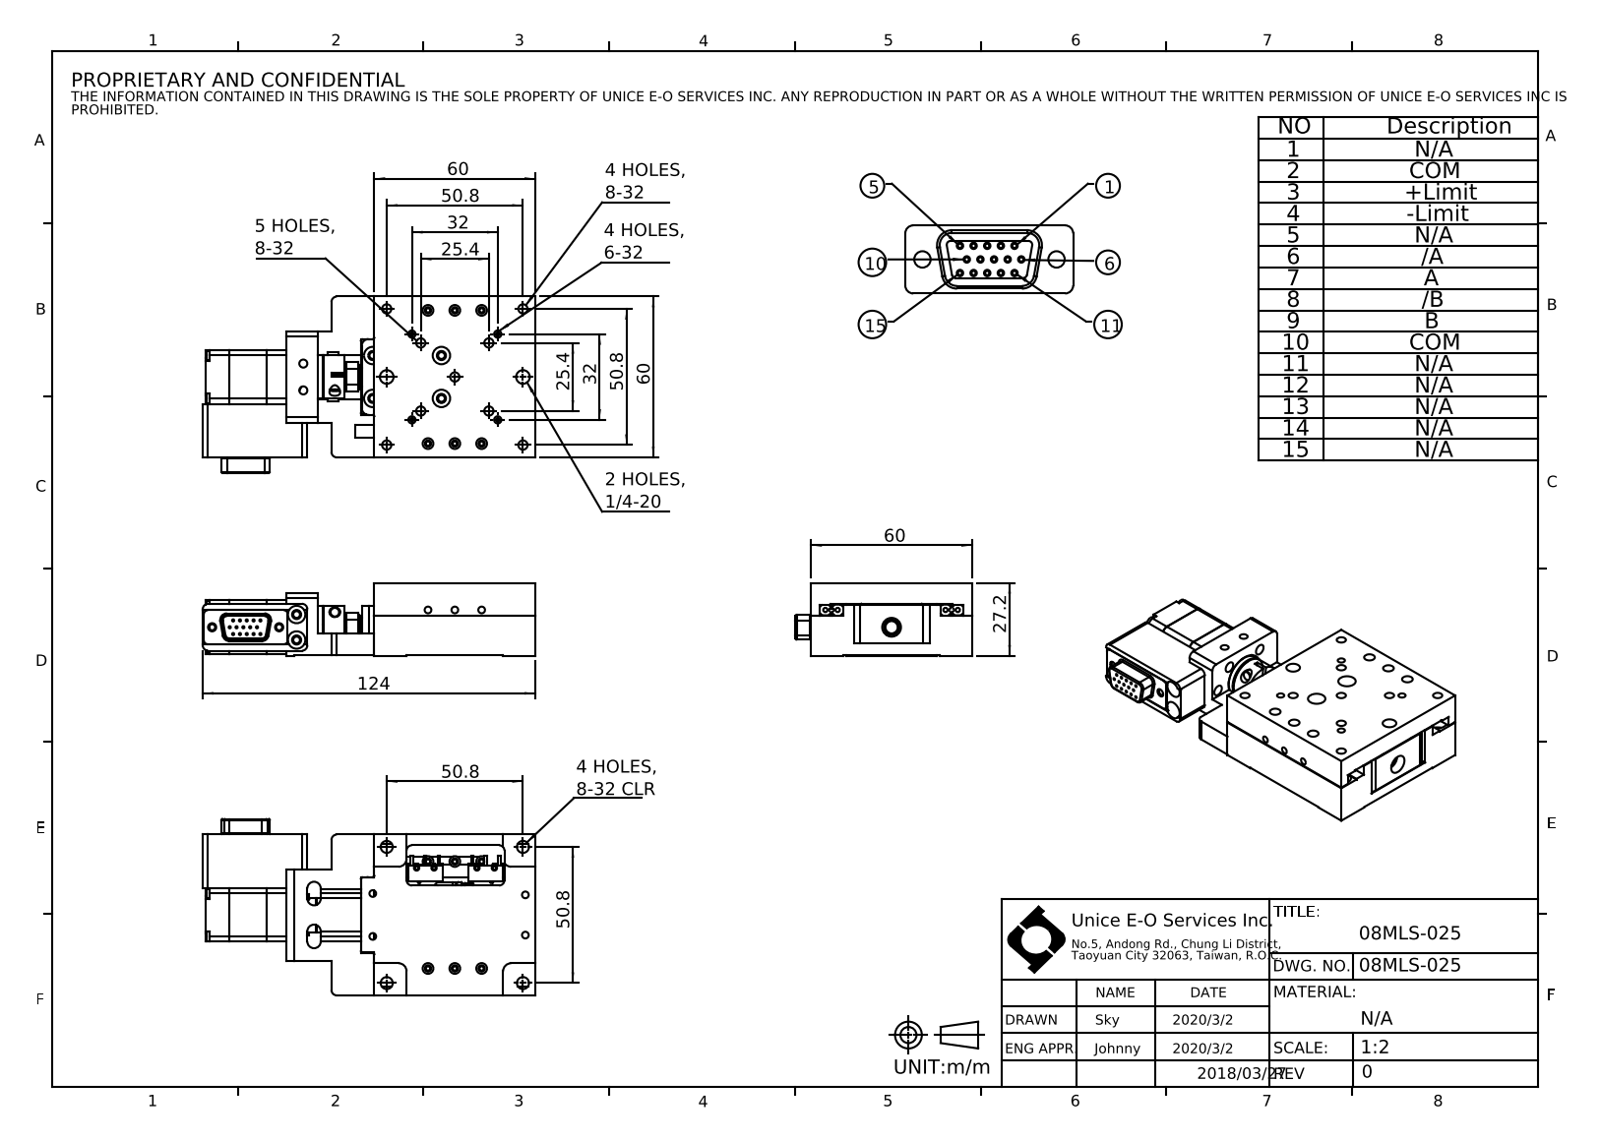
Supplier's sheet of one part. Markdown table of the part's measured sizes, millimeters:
| quantity | value |
| --- | --- |
| part name | 08MLS-025 |
| STEP written by | SolidWorks 2016 (CONFIG_CONTROL_DESIGN) |
| units | millimeters |
| bodies | 0 solids, 529 faces (232 planar, 278 cylindrical, 19 other) |
| overall size | 124 × 65.83 × 27.2 |
| round holes (diameter × count) | 0.8 × 15, 4 × 12, 2.5 × 9, 3.45 × 9, 6.5 × 7, 7.2 × 6, 2 × 4, 2.71 × 4, 4.5 × 4, 3 × 3, 2.26 × 2, 2.6 × 2 |
| round bosses / shafts (diameter × count) | 3.6 × 4, 5.4 × 2, 4 × 2, 16 × 1, 14.8 × 1, 8 × 1, 6 × 1, 3.68 × 1 |
| partial cylindrical surfaces (radius × count) | 2 × 18, 2.5 × 9, 0.5 × 8, 1 × 4, 1.5 × 4, 3 × 4, 1.8 × 2, 6.25 × 1 |
| main face-to-face distances | 27, 19.2, 7.8, 60, 4, 4.3, 44.15, 15.85, 20, 18.9 |
| hole center spacings | 2.84, 4.58, 5.08, 2.54, 17.96, 40.16, 6.84, 25.4 |
